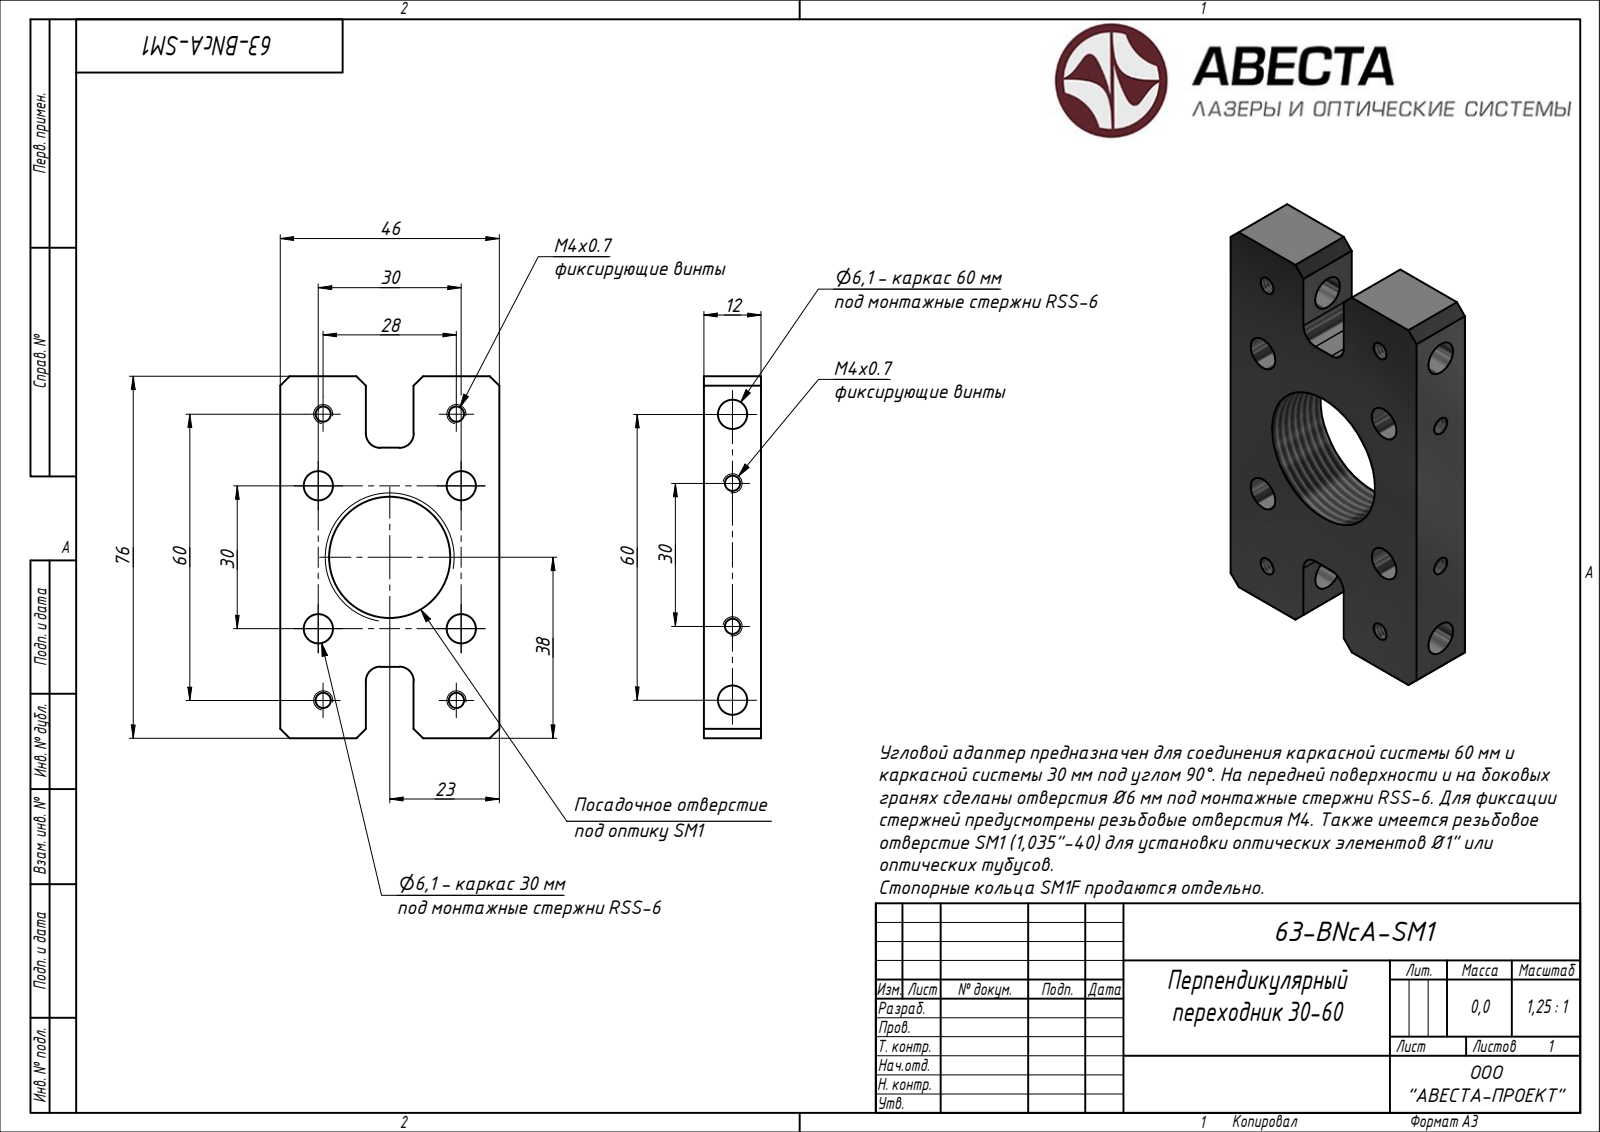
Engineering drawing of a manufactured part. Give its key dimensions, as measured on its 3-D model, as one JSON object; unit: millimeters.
{"step_written_by": "ST-DEVELOPER v15 (AUTOMOTIVE_DESIGN)", "units": "millimeters", "bodies": {"solids": 1, "faces": 60, "planar": 22, "cylindrical": 0, "other": 38}, "overall_size": [76, 46, 12], "volume_mm3": 28338, "surface_area_mm2": 11825, "face_to_face_distances": [12, 46, 18, 28, 76, 10, 19.8, 63.63, 15, 61]}
